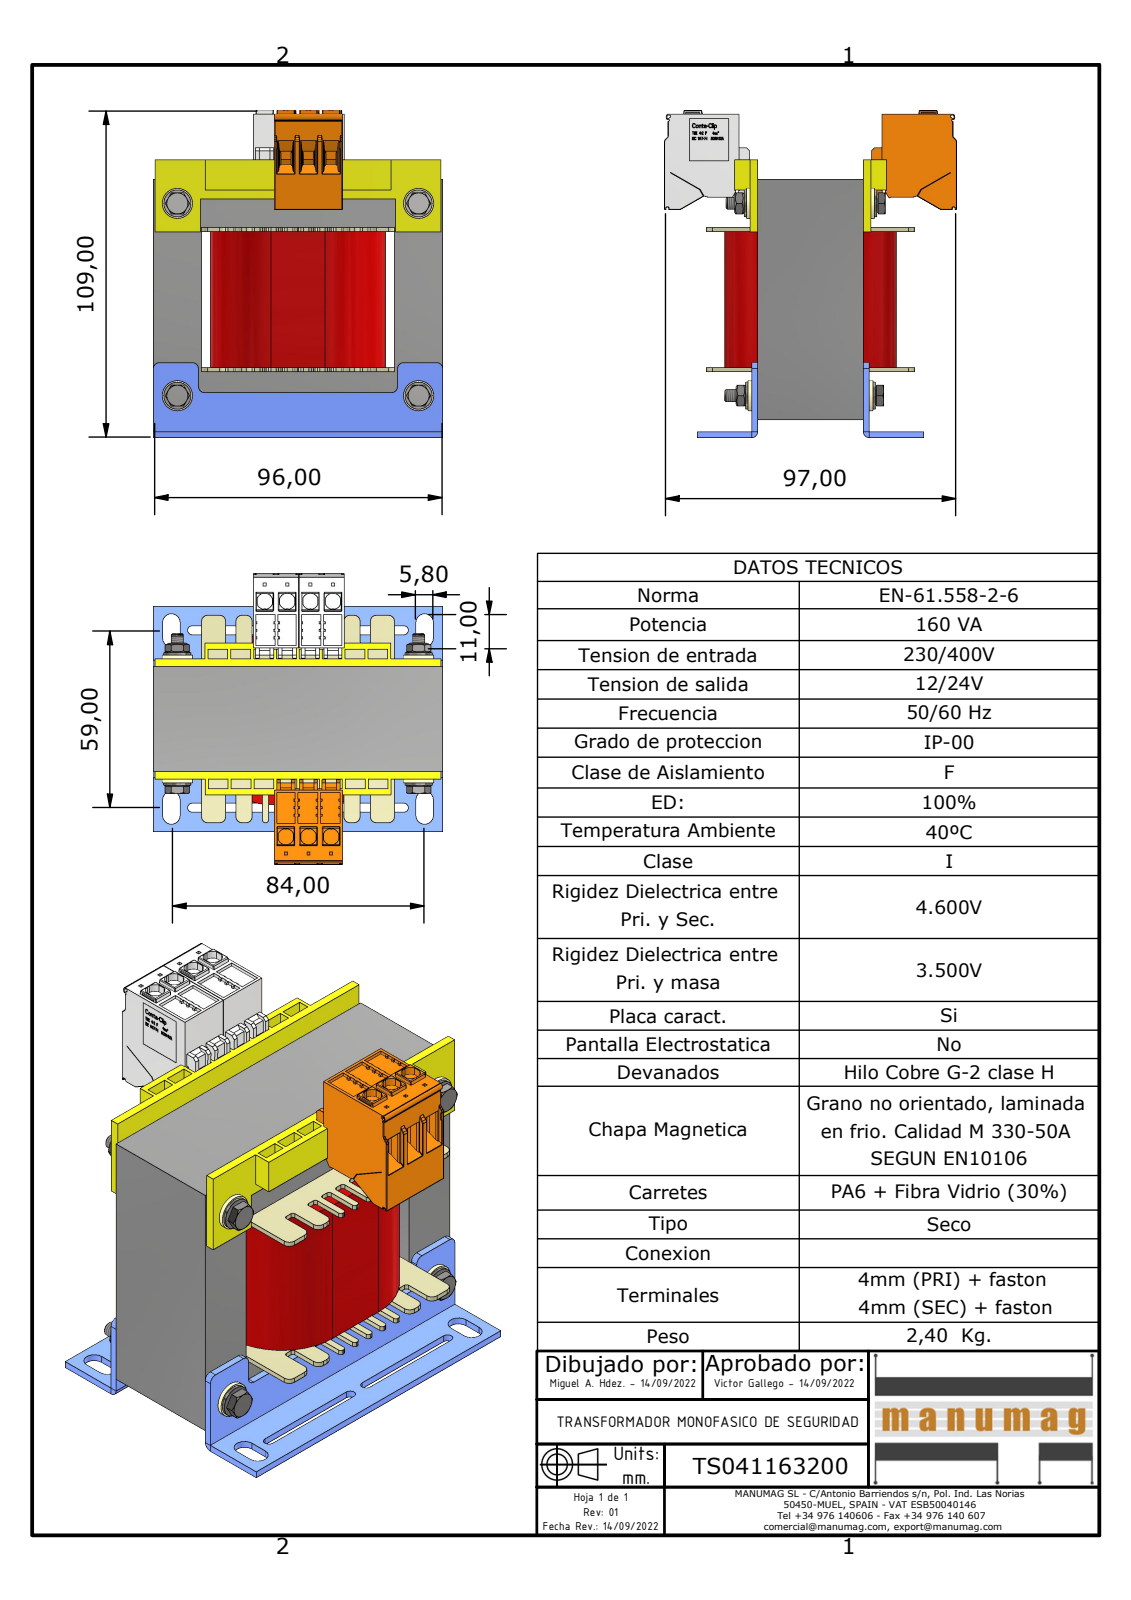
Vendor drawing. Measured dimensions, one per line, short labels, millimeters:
name: TS041163200; EI96 x 80 - 35 (RC32); AF32DIN; EI 96 X 80 - 35 (+7 more)
written by: Autodesk Inventor 2023 (AUTOMOTIVE_DESIGN)
unit: mm
bodies: 33 solids, 5982 faces (4778 planar, 833 cylindrical, 371 other)
size: 109 × 96.9 × 96
volume: 358 671 mm³; area: 114 882 mm²
holes: 4× ⌀3.24, 4× ⌀4, 4× ⌀4.3, 4× ⌀5.5, 2× ⌀5.8
bosses: 4× ⌀10, 4× ⌀9, 4× ⌀5.9, 4× ⌀4.9, 4× ⌀3.62
rounds: 271× R0.15, 86× R0.2, 52× R0.8, 22× R0.5, 22× R2, 12× R0.3, 8× R1, 8× R1.5
face distances: 64, 16, 35, 32, 48, 2, 80, 0.5, 2.5, 4
hole spacings: 64, 80, 102.45
